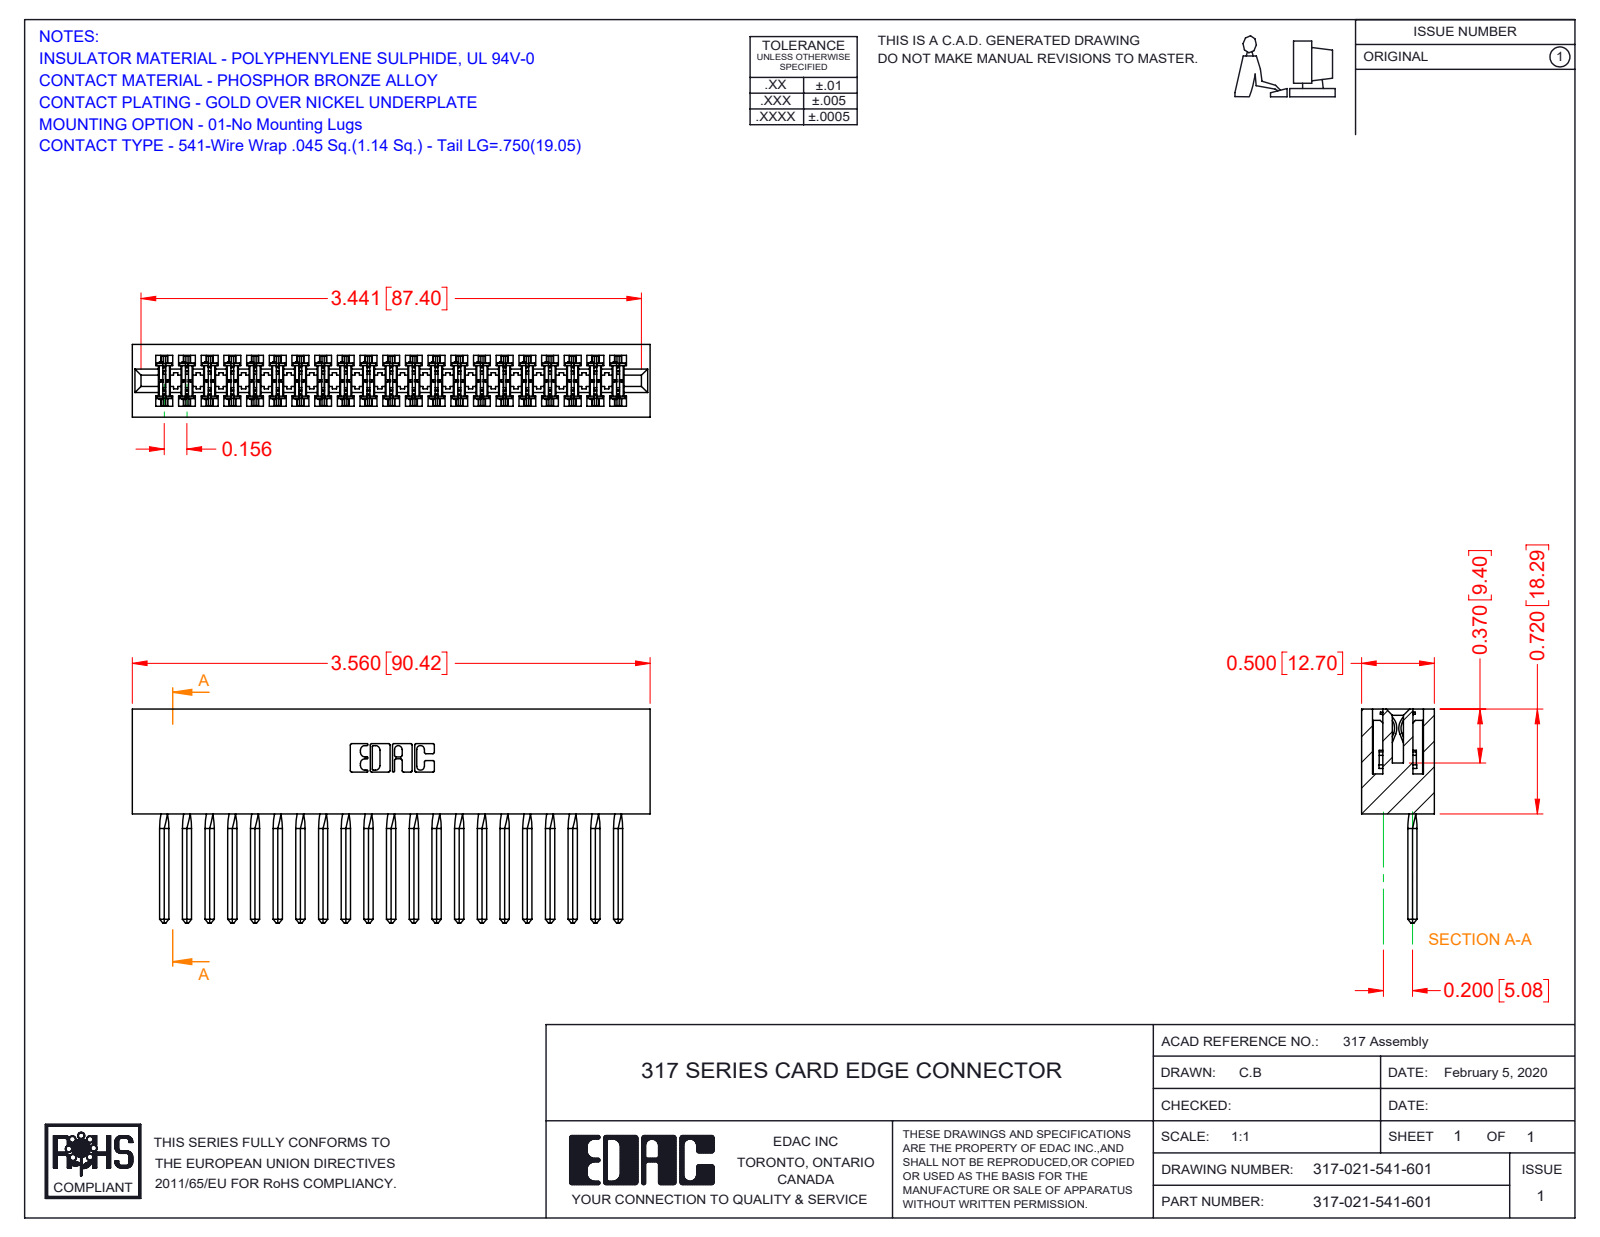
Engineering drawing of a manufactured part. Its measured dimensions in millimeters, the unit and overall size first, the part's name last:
Units: millimetres
Overall size (bounding box): 90.4 × 37.3 × 12.7
Partial cylindrical surfaces — rounded edges, fillets, slot ends (radius × count): R0.4 ×42, R0.3 ×22, R0.2 ×6, R0.8 ×6, R0.7 ×3, R2.4 ×2, R2.5 ×2, R2.8 ×2
Main face-to-face distances: 12.7, 1.9, 10.8, 2.8, 8.9, 5, 19.6, 5.6, 16.8, 18.3
Volume: 15 700 mm³ · Surface area: 21 710 mm²
Bodies: 22 solids, 3282 faces (2654 planar, 544 cylindrical, 84 other)
Part name (STEP PRODUCT): 317-290-002_541; 317 Part_Lugless; 317-021-541-601
STEP written by: SolidWorks 2016 (CONFIG_CONTROL_DESIGN)
